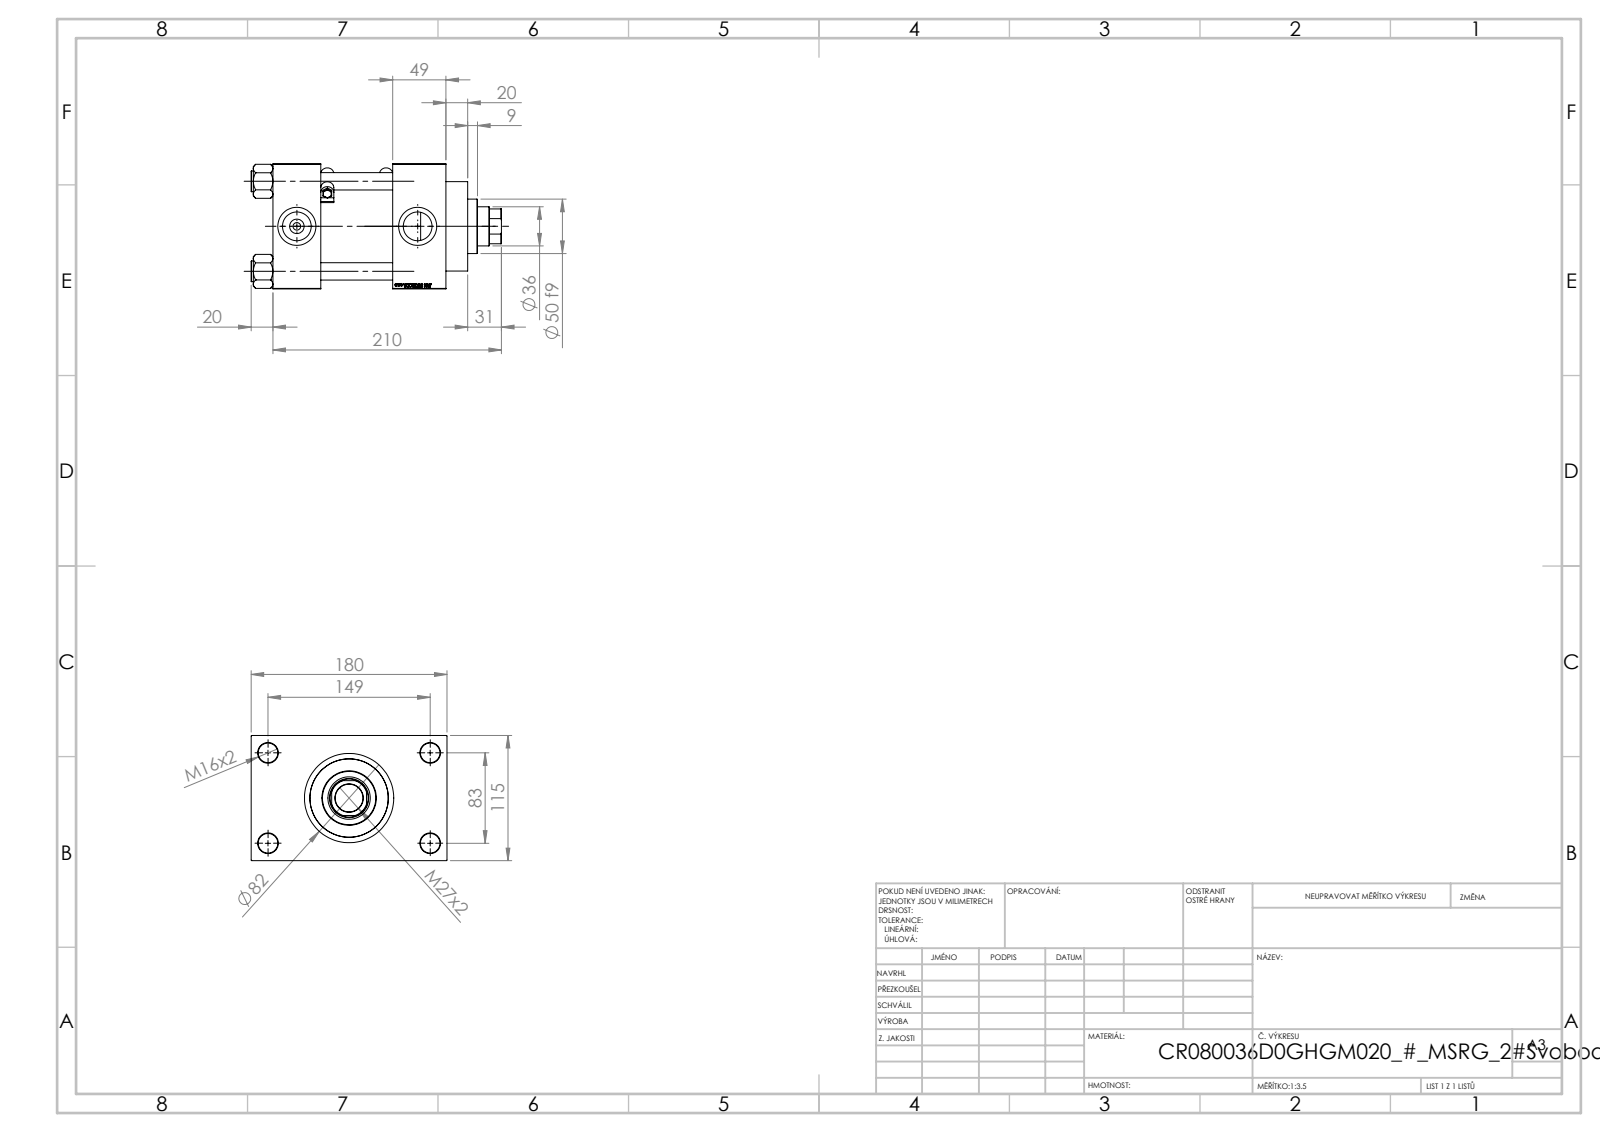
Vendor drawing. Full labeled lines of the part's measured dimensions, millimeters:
Part name (STEP PRODUCT): V215CR_D_Body; V215CR_VCP_D; MSRF_MSRG1; V215CR_D_TYCINKA (+2 more)
STEP written by: SolidWorks 2019 (CONFIG_CONTROL_DESIGN)
Units: millimetres
Bodies: 13 solids, 1215 faces (581 planar, 116 cylindrical, 518 other)
Overall size (bounding box): 230 × 180 × 115
Volume: 1 987 000 mm³ · Surface area: 301 303 mm²
Round holes (diameter × count): ⌀16 ×4, ⌀18 ×4, ⌀7 ×2, ⌀26.44 ×2, ⌀35 ×2, ⌀25.5 ×1, ⌀36 ×1, ⌀39 ×1, ⌀61 ×1, ⌀72 ×1, ⌀80 ×1
Round bosses / shafts (diameter × count): ⌀19 ×4, ⌀5 ×2, ⌀2.5 ×2, ⌀86 ×1, ⌀82 ×1, ⌀50 ×1
Partial cylindrical surfaces — rounded edges, fillets, slot ends (radius × count): R0.5 ×12, R6 ×4, R17.5 ×1
Main face-to-face distances: 115, 66, 110, 49, 44, 159, 32.5, 147.5, 20, 69
Hole centre spacings: 33.15, 58.48, 82.7, 85.28, 89.24, 115.85, 142.43, 83
